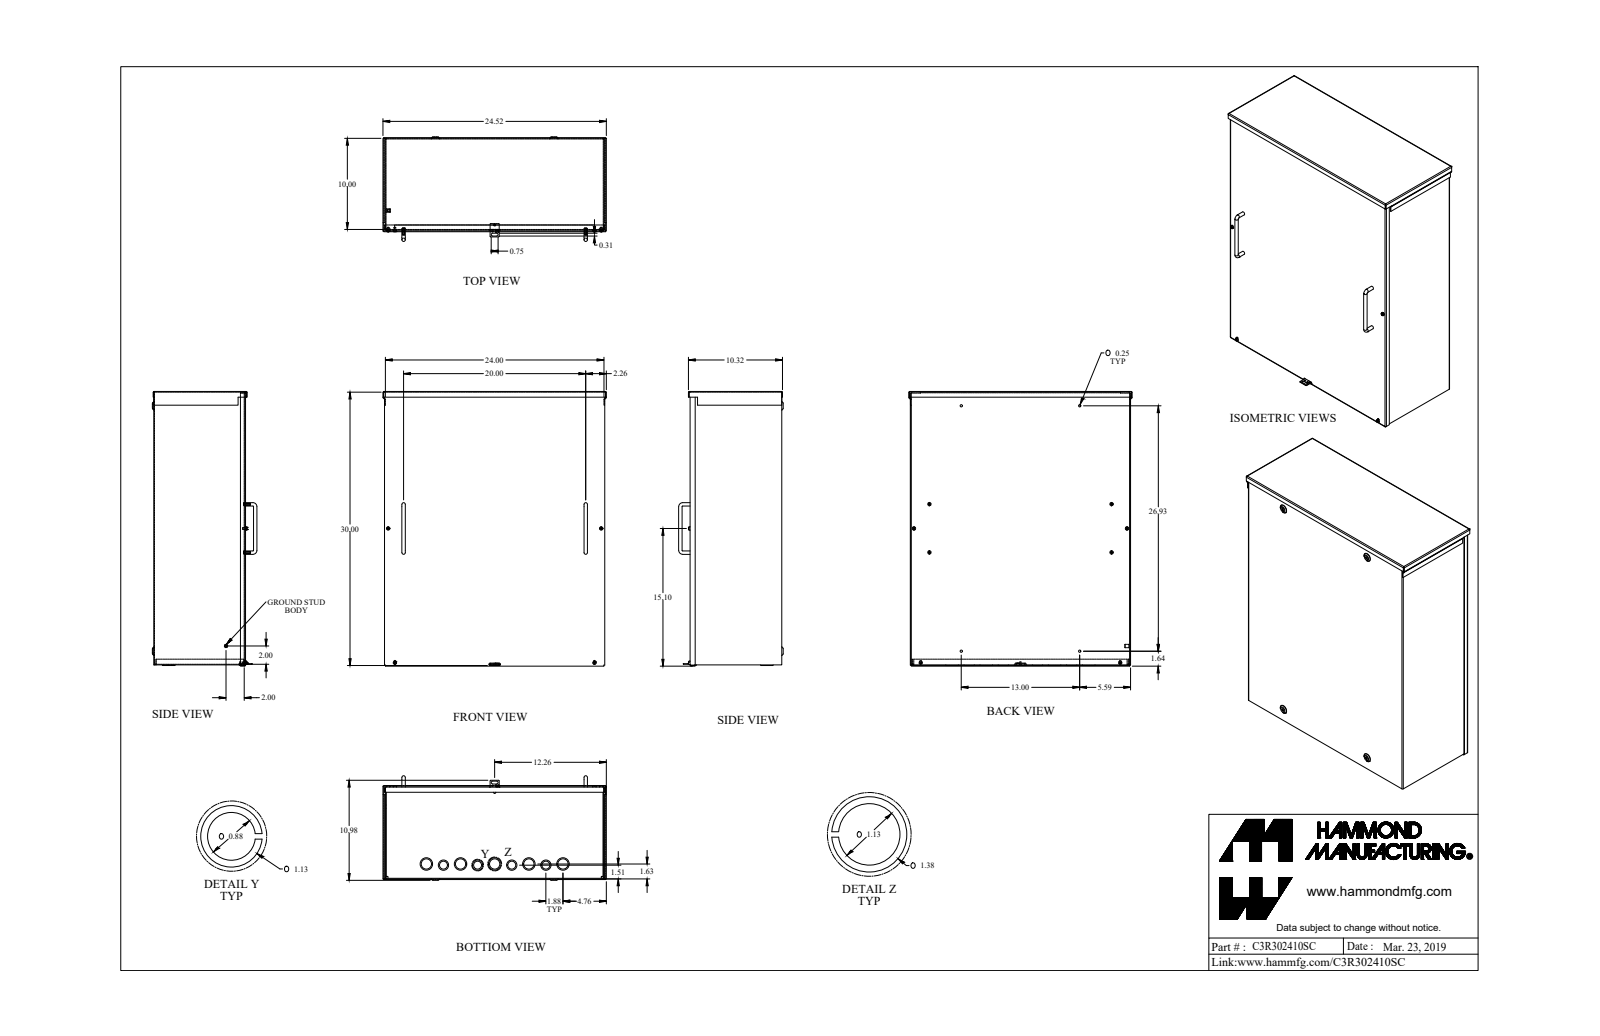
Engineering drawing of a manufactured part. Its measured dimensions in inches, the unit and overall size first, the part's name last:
Units: inches
Overall size (bounding box): 30.135 × 24.519 × 11.478
Round holes (diameter × count): ⌀0.156 ×5, ⌀0.17 ×4, ⌀0.203 ×4, ⌀0.25 ×4, ⌀0.875 ×4, ⌀1.125 ×3, ⌀1.125 ×2, ⌀0.125 ×1, ⌀0.137 ×1
Round bosses / shafts (diameter × count): ⌀0.375 ×9, ⌀0.19 ×8, ⌀1.375 ×5, ⌀1.125 ×4, ⌀0.367 ×4, ⌀0.375 ×2, ⌀0.125 ×1
Partial cylindrical surfaces — rounded edges, fillets, slot ends (radius × count): R0.036 ×20, R0.108 ×20, R0.109 ×8, R0.125 ×8, R0.156 ×2, R0.029 ×1, R0.086 ×1
Main face-to-face distances: 0.072, 10, 9.928, 10.072, 23.928, 24, 23.856, 0.072, 29.856, 29.928
Hole centre spacings: 20, 3.75, 7.5, 0.024, 1.879, 1.88, 3.146, 5.3
Volume: 195.4 in³ · Surface area: 5 430 in²
Bodies: 17 solids, 609 faces (314 planar, 177 cylindrical, 118 other)
Part name (STEP PRODUCT): C3R302410SC_Default
STEP written by: SolidWorks 2019 (CONFIG_CONTROL_DESIGN)
